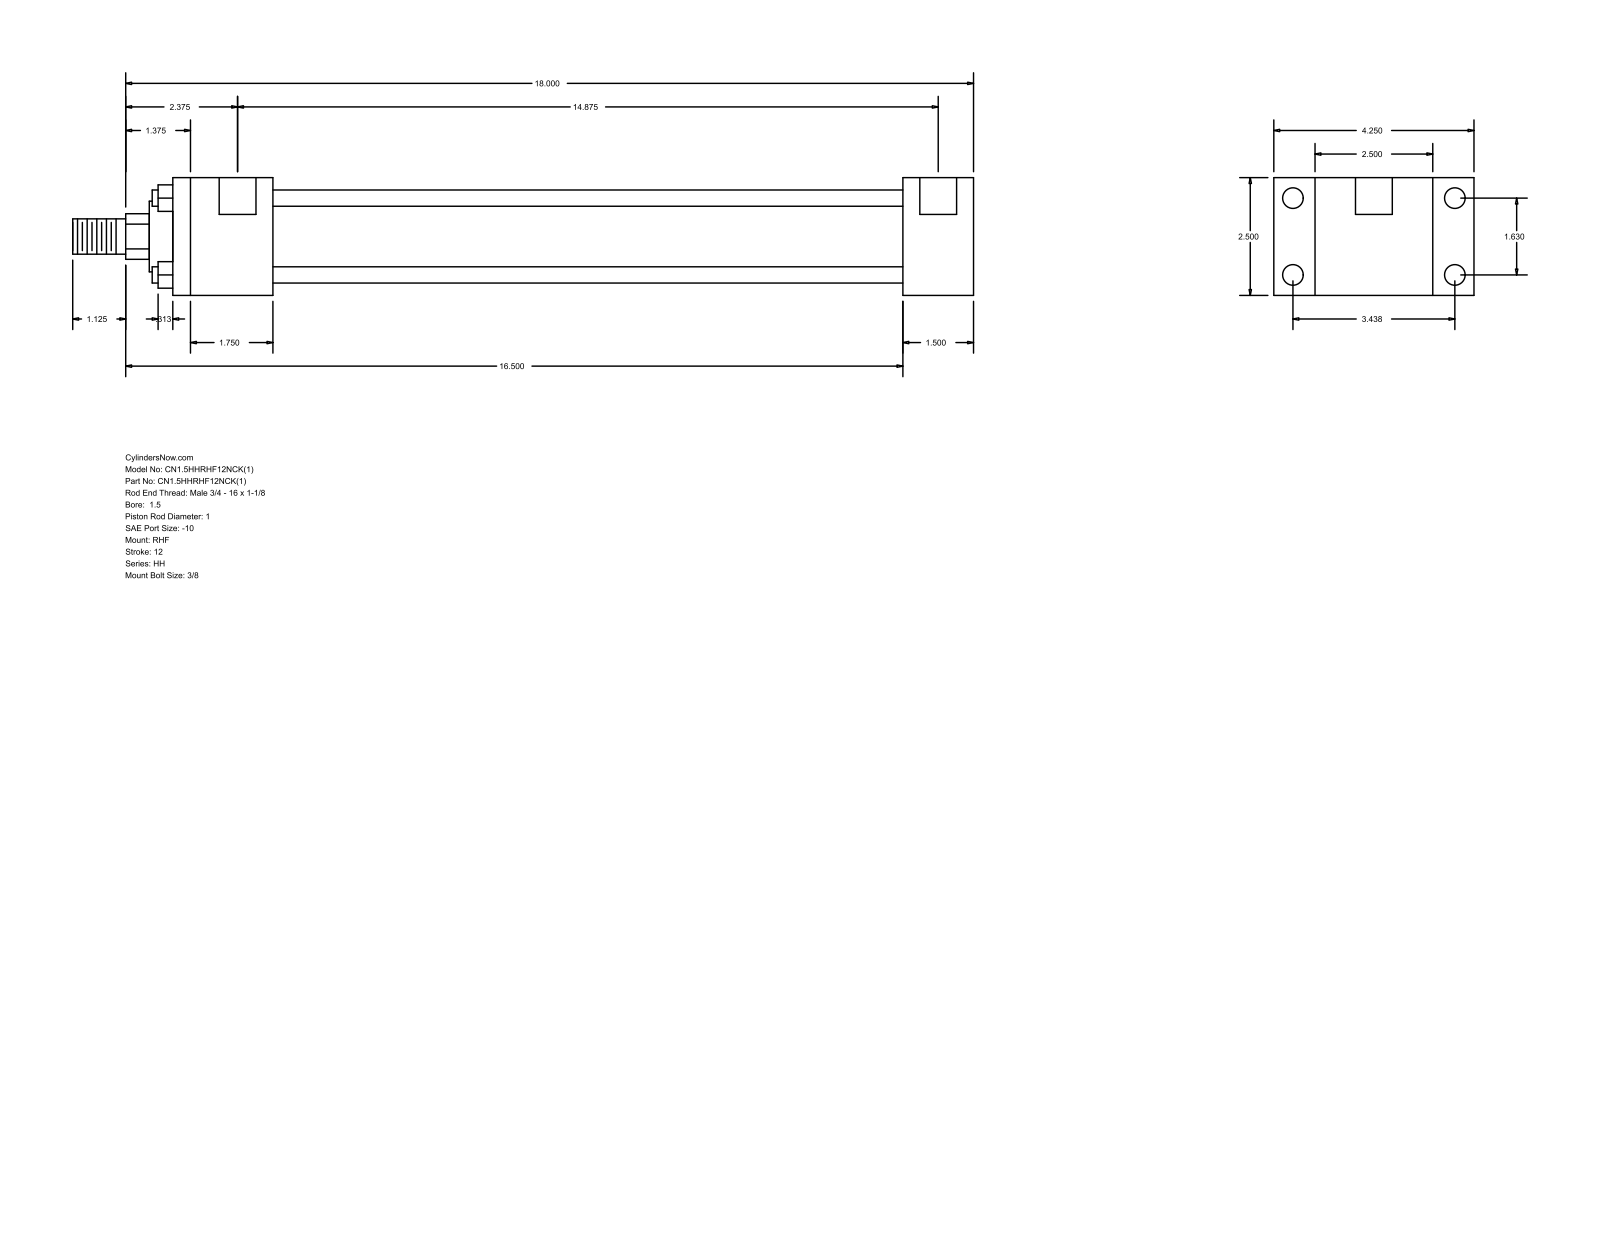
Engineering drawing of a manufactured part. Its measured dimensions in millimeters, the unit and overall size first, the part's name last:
Units: millimetres
Overall size (bounding box): 485.77 × 107.95 × 63.5
Round holes (diameter × count): ⌀5.56 ×4, ⌀11.13 ×4, ⌀19.84 ×2
Round bosses / shafts (diameter × count): ⌀8.76 ×4, ⌀44.45 ×1, ⌀38.1 ×1, ⌀25.4 ×1, ⌀19.05 ×1
Partial cylindrical surfaces — rounded edges, fillets, slot ends (radius × count): R12.29 ×1
Main face-to-face distances: 63.5, 22.23, 85.73, 38.1, 107.96, 339.72, 377.82, 53.98, 393.7, 431.8
Hole centre spacings: 1.59, 41.4, 87.32, 96.64, 379.41, 381, 377.82
Bodies: 0 solids, 88 faces (60 planar, 28 cylindrical, 0 other)
Part name (STEP PRODUCT): HH_RHF__0150_1
STEP written by: GSSL Pune (CONFIG_CONTROL_DESIGN)
